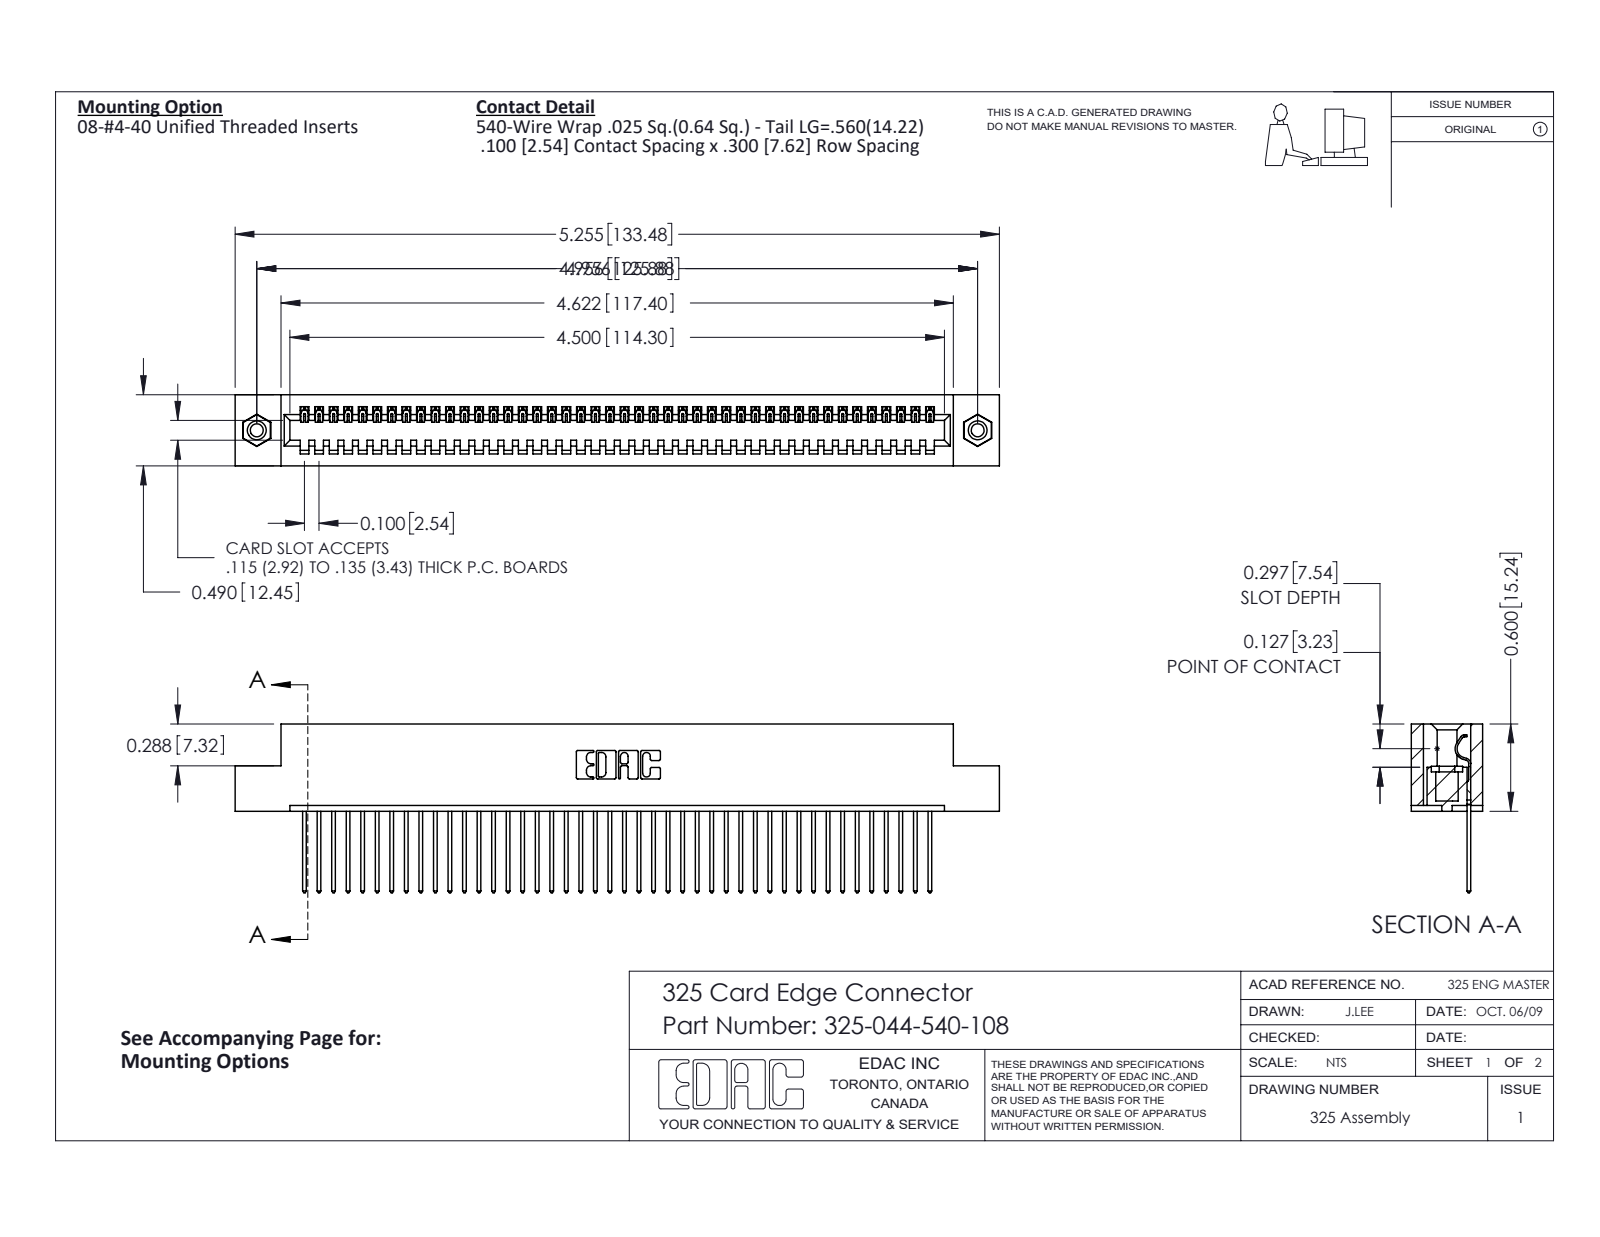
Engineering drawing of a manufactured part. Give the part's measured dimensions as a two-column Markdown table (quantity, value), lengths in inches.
| quantity | value |
| --- | --- |
| part name | 325 Part_TI; 325-044-540-108; 325-292-001_325-293-140; 345-250-001_345-250-003-102 |
| STEP written by | SolidWorks 2016 (CONFIG_CONTROL_DESIGN) |
| units | inches |
| bodies | 47 solids, 2726 faces (1950 planar, 760 cylindrical, 16 other) |
| overall size | 5.255 × 1.16 × 0.49 |
| volume | 1.038 in³ |
| surface area | 29.57 in² |
| round holes (diameter × count) | 0.089 × 2, 0.125 × 2, 0.16 × 2 |
| round bosses / shafts (diameter × count) | 0.155 × 2 |
| partial cylindrical surfaces (radius × count) | 0.006 × 88, 0.01 × 88, 0.01 × 22, 0.007 × 6, 0.031 × 6, 0.026 × 3, 0.014 × 1, 0.022 × 1 |
| main face-to-face distances | 0.083, 0.407, 0.49, 0.3, 0.107, 0.383, 0.025, 0.325, 0.56, 0.04 |
| hole center spacings | 4.956 |
